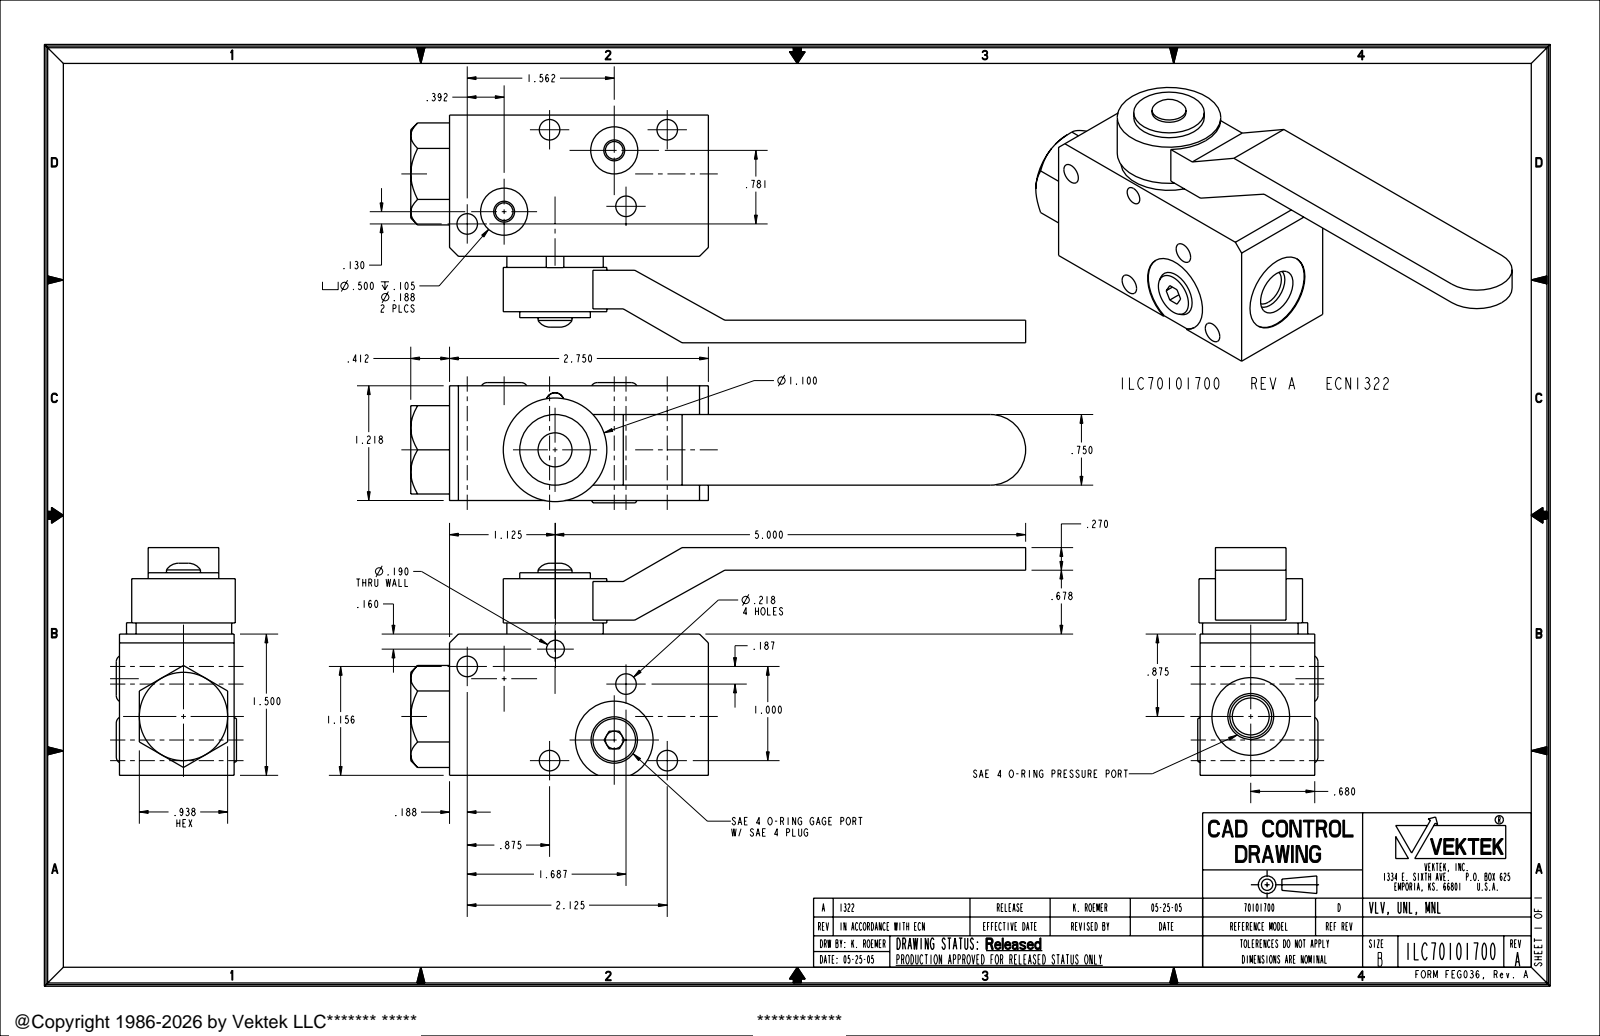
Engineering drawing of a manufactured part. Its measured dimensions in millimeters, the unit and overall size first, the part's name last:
Units: millimetres
Overall size (bounding box): 165.9 × 61.4 × 32.4
Round holes (diameter × count): ⌀5.5 ×4, ⌀4.8 ×2, ⌀4.8 ×2, ⌀10 ×2, ⌀12.7 ×2, ⌀21 ×2, ⌀17.6 ×1
Round bosses / shafts (diameter × count): ⌀27.9 ×1, ⌀26 ×1, ⌀19.1 ×1, ⌀11.1 ×1, ⌀9.6 ×1, ⌀9.2 ×1, ⌀4.7 ×1
Partial cylindrical surfaces — rounded edges, fillets, slot ends (radius × count): R9.5 ×1
Main face-to-face distances: 30.9, 61.4, 38.1, 23.3, 55.3, 17.2, 6.1, 7.7, 23.2, 26.8
Hole centre spacings: 10.5, 13, 15.3, 15.4, 16, 18.3, 21.3, 23.5
Volume: 103 900 mm³ · Surface area: 26 540 mm²
Bodies: 3 solids, 138 faces (54 planar, 48 cylindrical, 36 other)
Part name (STEP PRODUCT): ILC70101700
STEP written by: PRO/ENGINEER BY PARAMETRIC TECHNOLOGY CORPORATION, 2004290 (AUTOMOTIVE_DESIGN_CC2)
